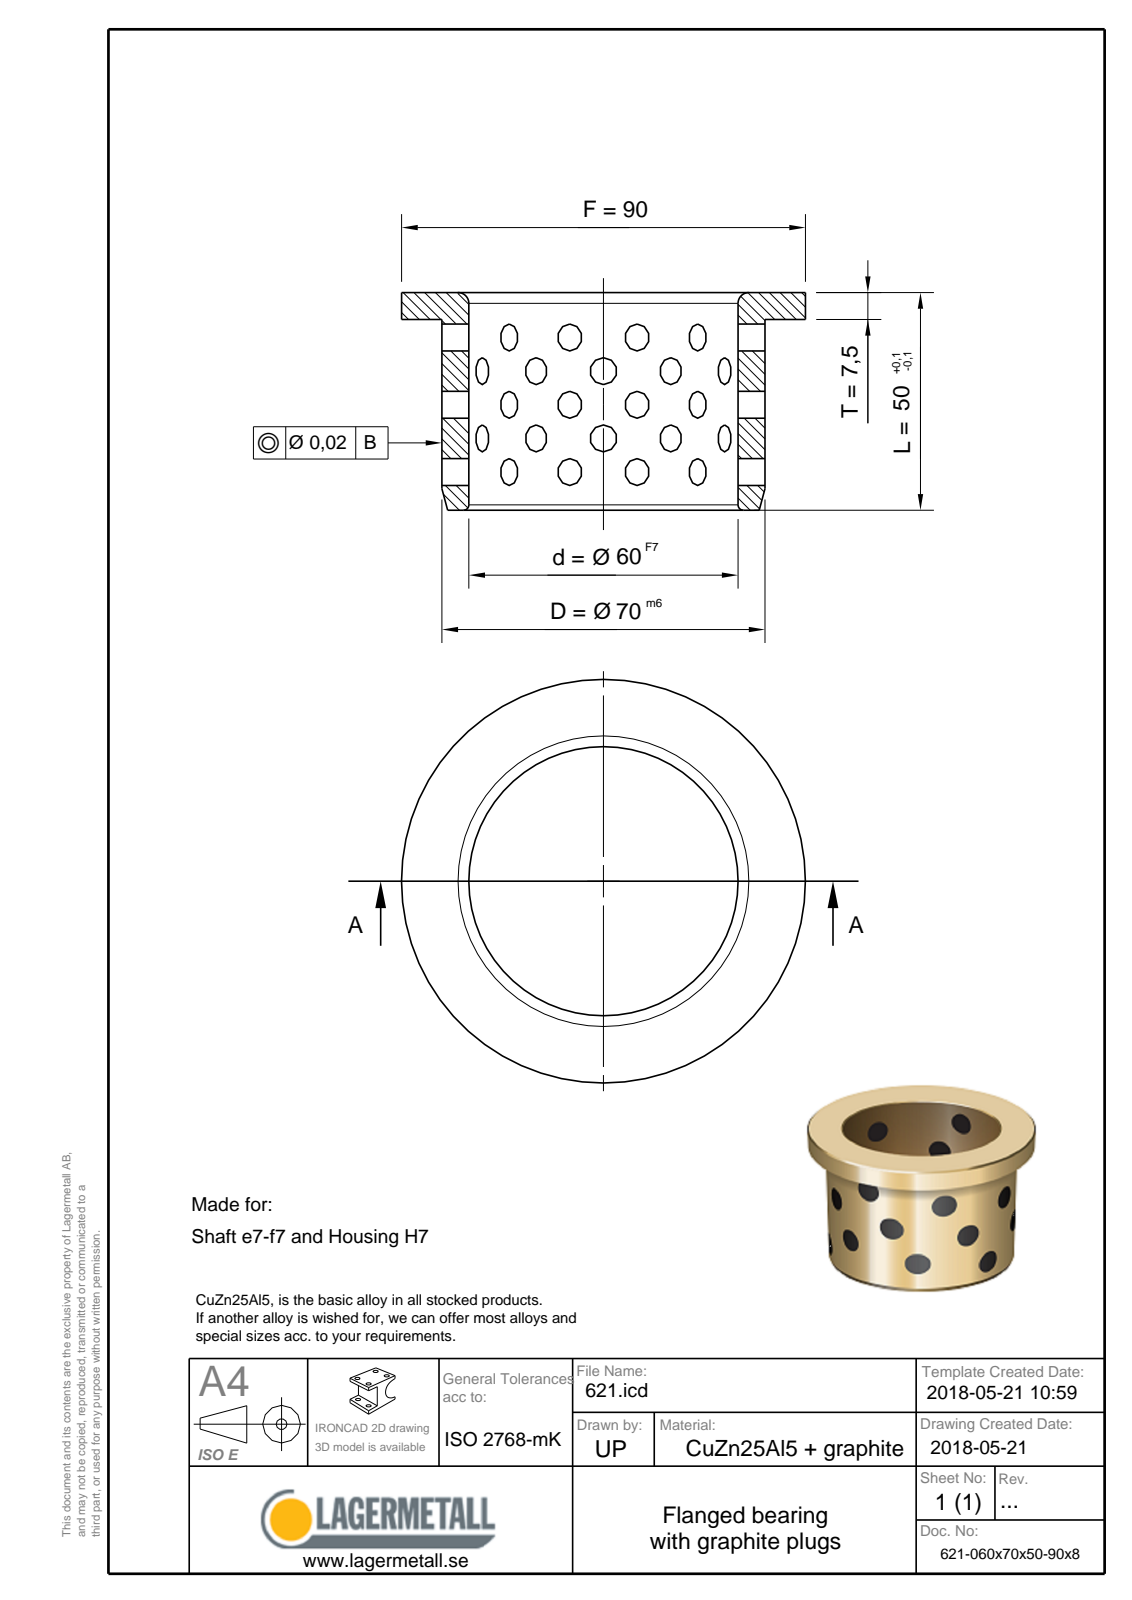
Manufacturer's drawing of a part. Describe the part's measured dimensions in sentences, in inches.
The part is named "621-060x70x50-90x8". Its 3-D file was written by "Spatial InterOp 3D (CONFIG_CONTROL_DESIGN)". It is 1 solid with 9 faces: 3 planar, 3 cylindrical and 3 other. Overall it measures 3.543 by 3.543 by 1.969 inches. Its volume is 4.221 cubic inches and its surface area 42.42 square inches. Round holes: 1 of diameter 2.362. Round bosses or shafts: 1 of diameter 3.543, 1 of diameter 2.756. The main face-to-face distances are 0.295, 1.673, 1.969.
